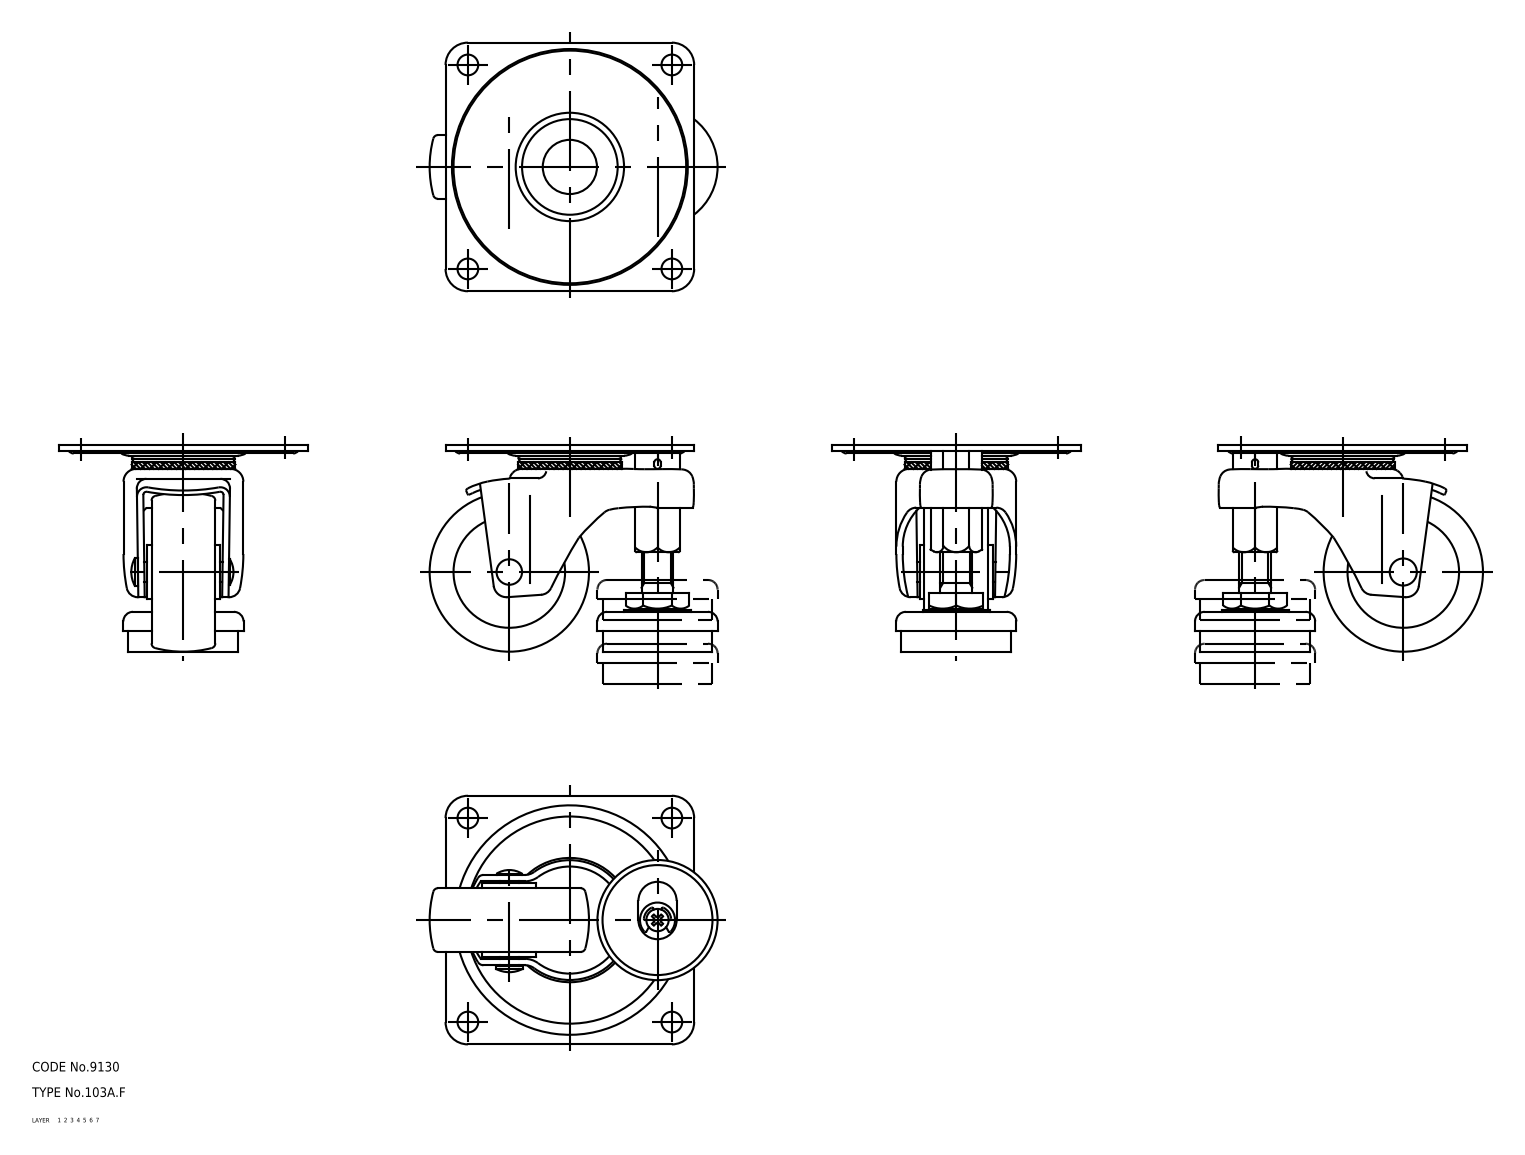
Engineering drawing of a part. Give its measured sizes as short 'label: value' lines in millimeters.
name: wheel; mounting plate; main shaft; foot (+2 more)
written by: CADfix (AUTOMOTIVE_DESIGN)
unit: mm
bodies: 6 solids, 320 faces (0 planar, 0 cylindrical, 320 other)
size: 90.35 × 78 × 65
volume: 83 959 mm³; area: 38 814 mm²
